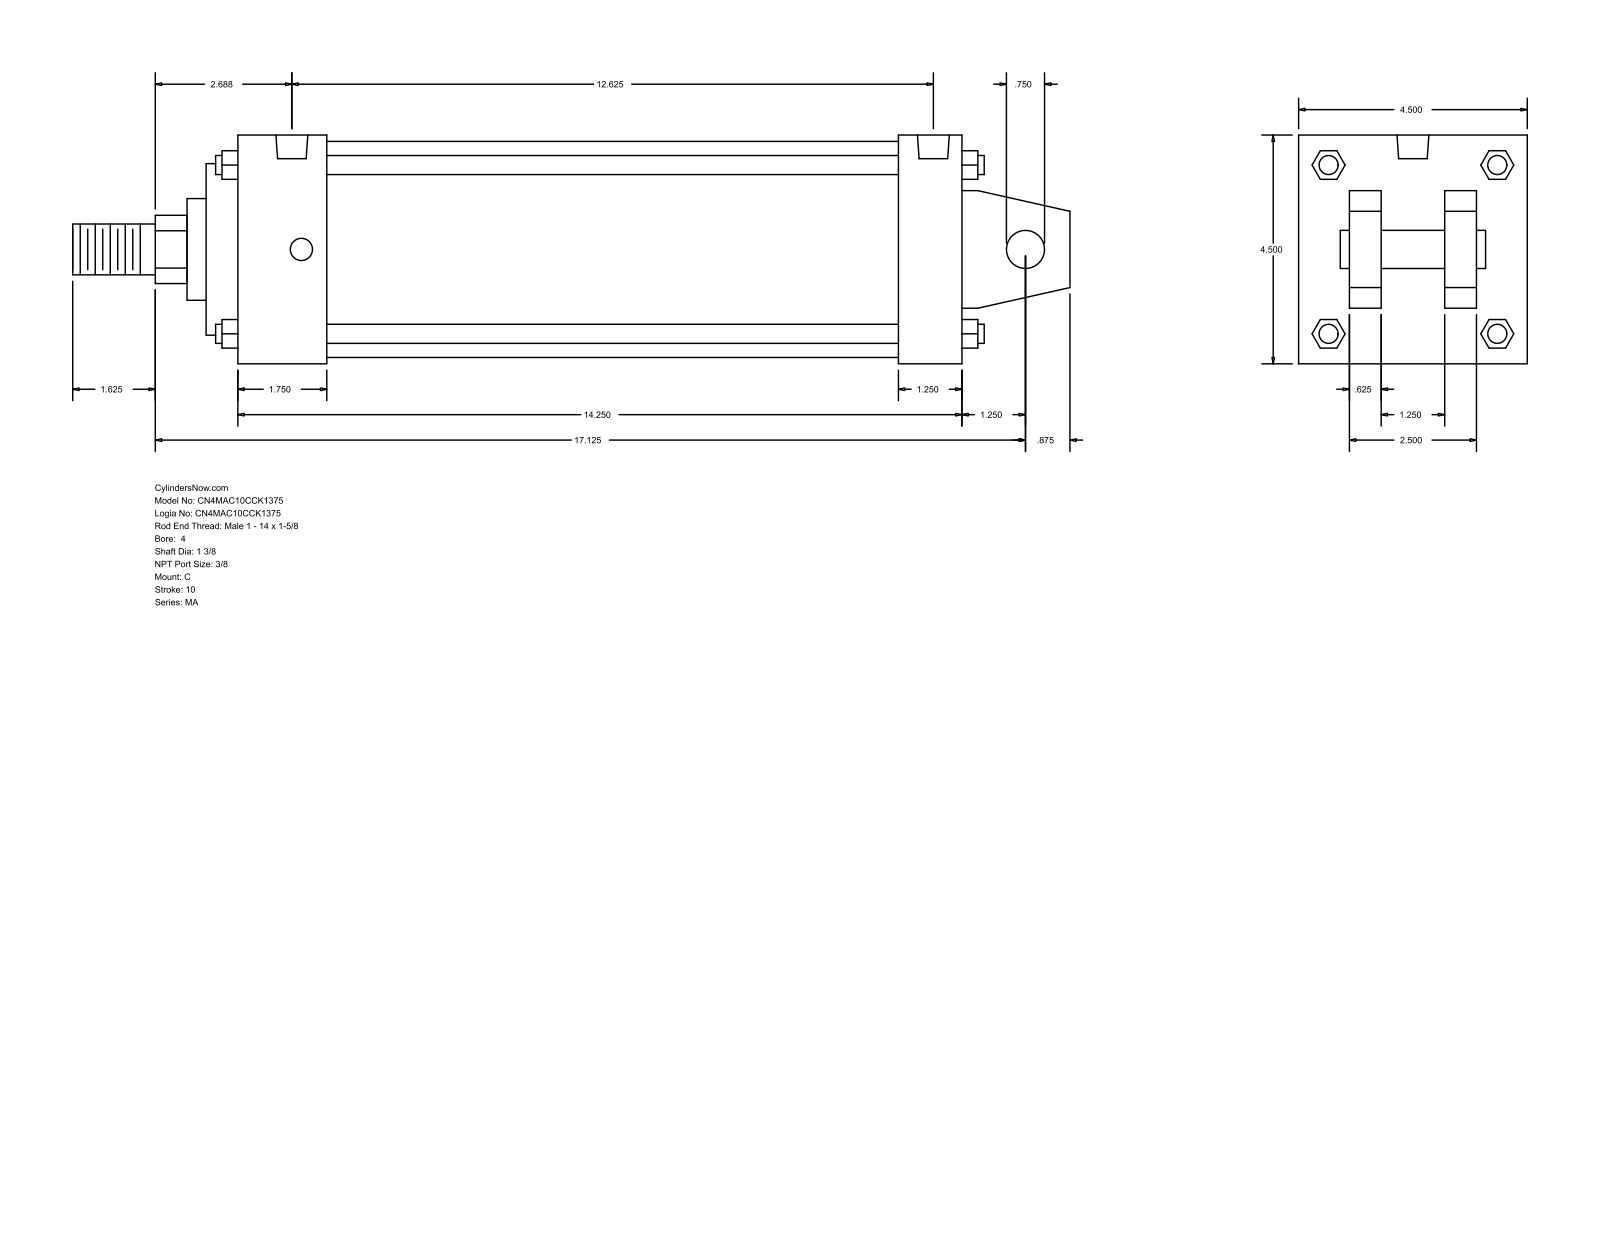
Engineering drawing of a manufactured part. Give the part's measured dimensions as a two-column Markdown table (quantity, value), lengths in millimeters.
| quantity | value |
| --- | --- |
| part name | MA_C__0400_1.375 |
| STEP written by | GSSL Pune (CONFIG_CONTROL_DESIGN) |
| units | millimeters |
| bodies | 0 solids, 141 faces (109 planar, 32 cylindrical, 0 other) |
| overall size | 498.48 × 114.3 × 114.3 |
| round holes (diameter × count) | 11.11 × 4, 15.93 × 2 |
| round bosses / shafts (diameter × count) | 9.53 × 4, 107.95 × 1, 85.72 × 1, 50.8 × 1, 34.92 × 1, 25.4 × 1, 19.05 × 1 |
| partial cylindrical surfaces (radius × count) | 17.06 × 1 |
| main face-to-face distances | 114.3, 15.87, 361.96, 73.03, 41.27, 25.4, 88.9, 47.63, 377.83, 346.08 |
| hole center spacings | 311.15, 4.76, 4.77, 315.91, 315.92, 320.68 |
